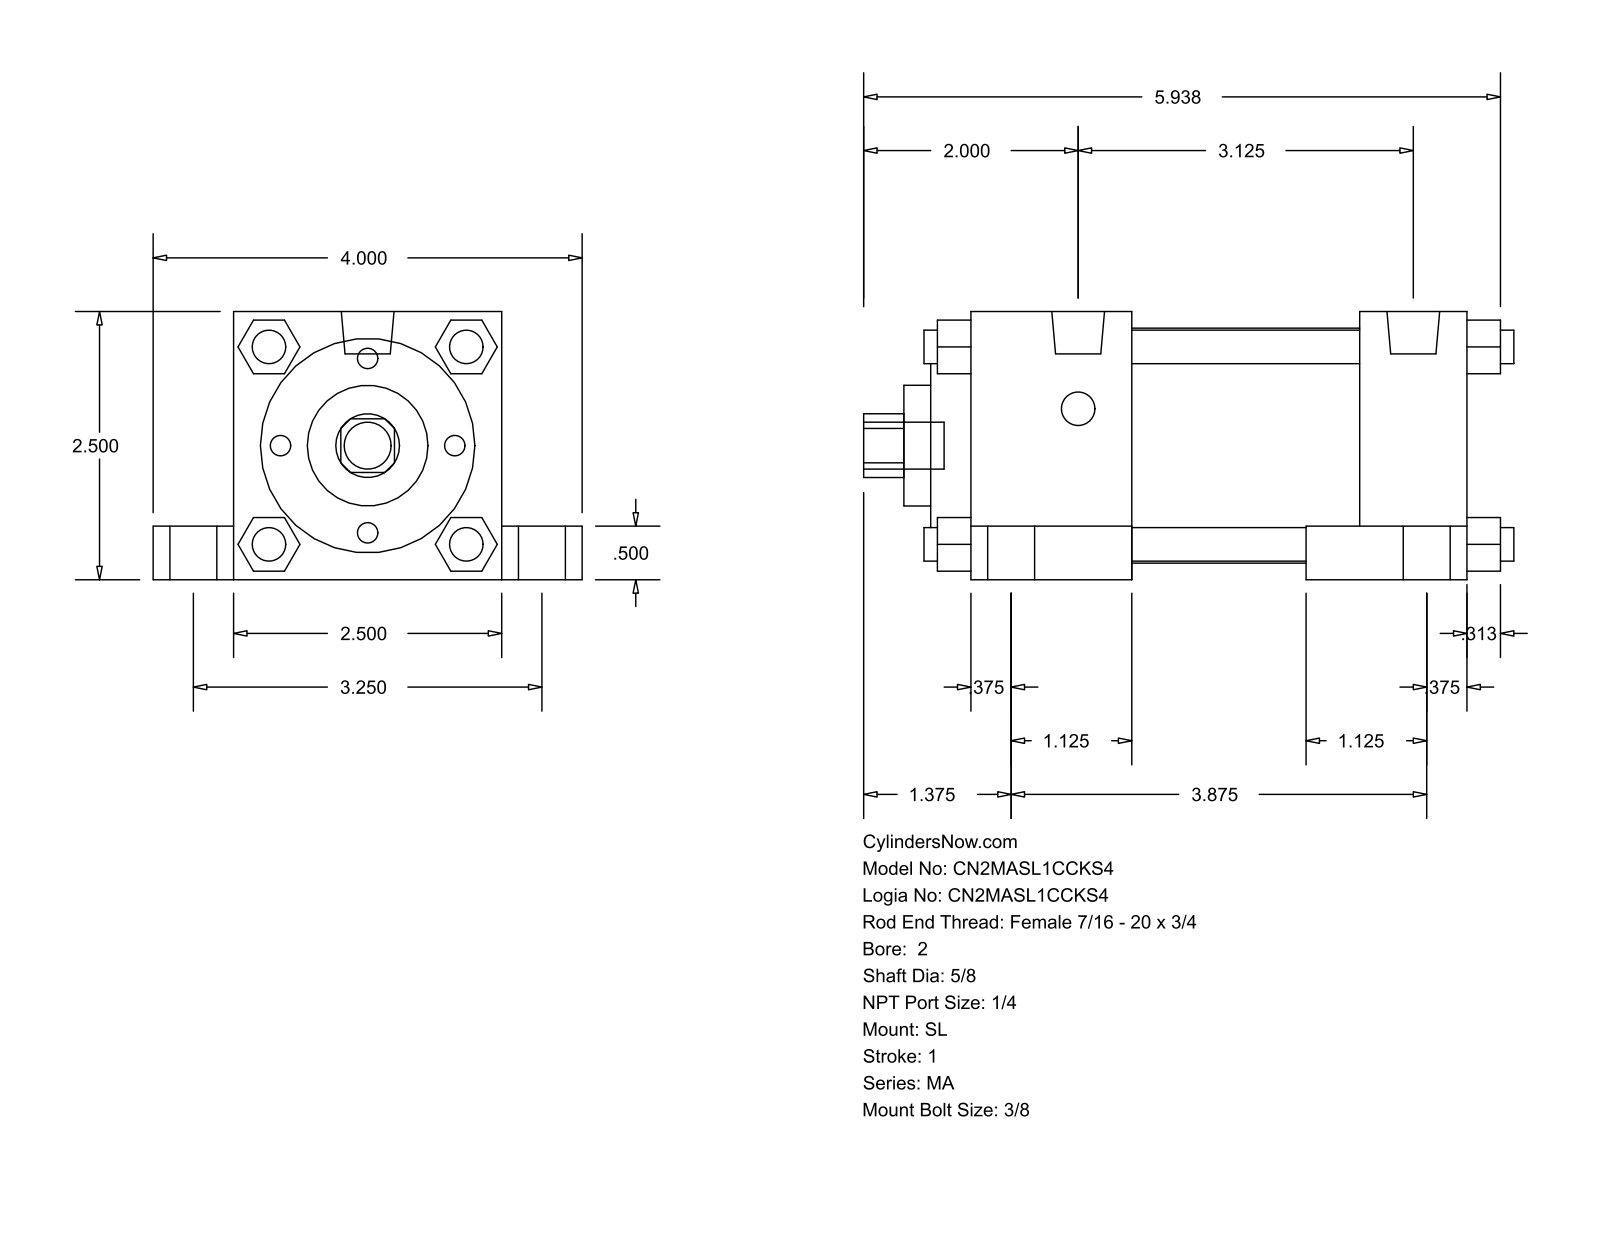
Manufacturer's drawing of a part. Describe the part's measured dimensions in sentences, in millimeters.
The part is named "MA_SL__0200_0.625". Its 3-D file was written by "GSSL Pune (CONFIG_CONTROL_DESIGN)". It is 0 solids with 150 faces: 113 planar, 37 cylindrical and 0 other. Overall it measures 153.99 by 101.6 by 63.5 millimeters. Round holes: 1 of diameter 15.88, 1 of diameter 28.57, 1 of diameter 50.8, 1 of diameter 55.63. Round bosses or shafts: 8 of diameter 7.94, 5 of diameter 11.11, 4 of diameter 17.46, 2 of diameter 12.49. Partial cylindrical surfaces (rounded edges, fillets, slot ends): 1 of radius 7.54. The main face-to-face distances are 63.5, 12.7, 53.97, 9.52, 19.05, 82.55, 38.1, 50.8, 117.48, 79.38.
